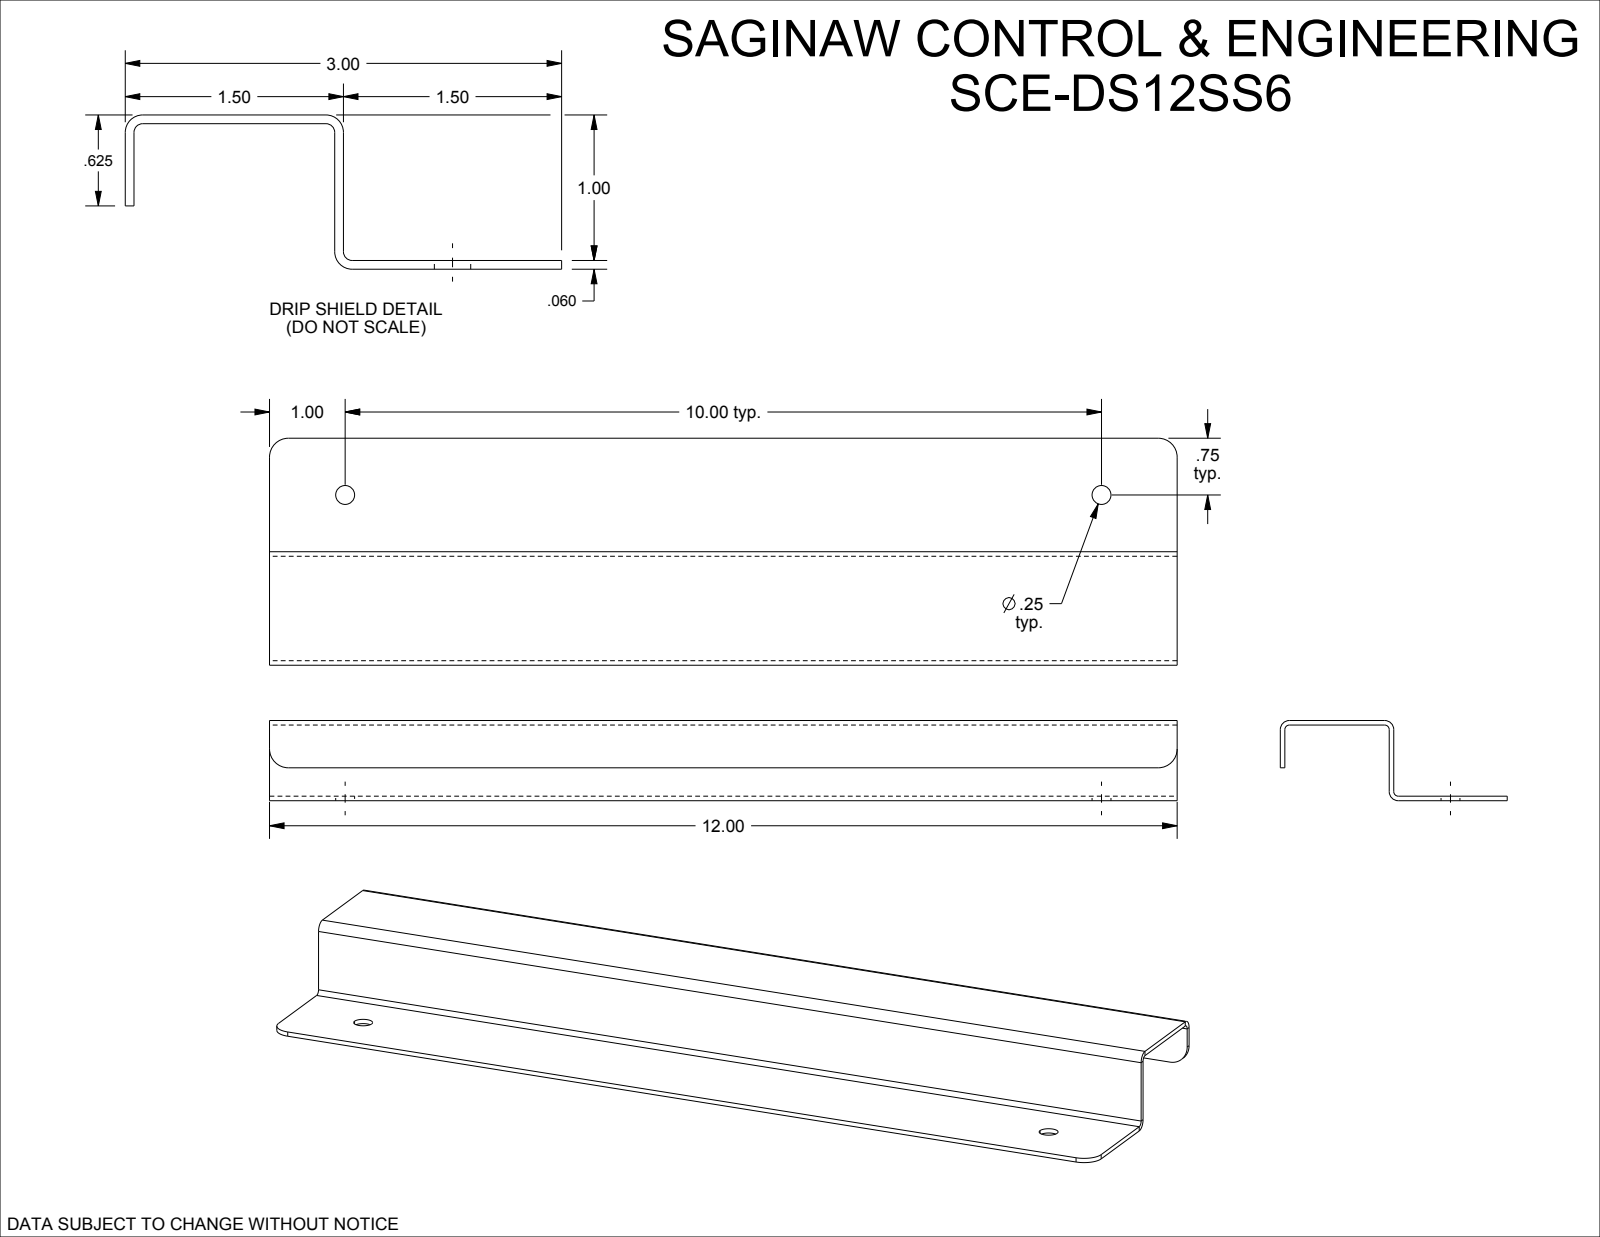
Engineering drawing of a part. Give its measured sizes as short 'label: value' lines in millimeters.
name: SCE-DS12SS6
written by: SolidWorks 2019 (CONFIG_CONTROL_DESIGN)
unit: mm
bodies: 1 solid, 24 faces (12 planar, 12 cylindrical, 0 other)
size: 304.8 × 76.2 × 26.9
volume: 52 340 mm³; area: 70 000 mm²
holes: 2× ⌀6.4
rounds: 4× R6.4, 3× R1.5, 3× R3
face distances: 1.5, 25.4, 26.9, 23.9, 36.6, 38.1, 35.1, 11, 9.5, 14.4
hole spacings: 254
